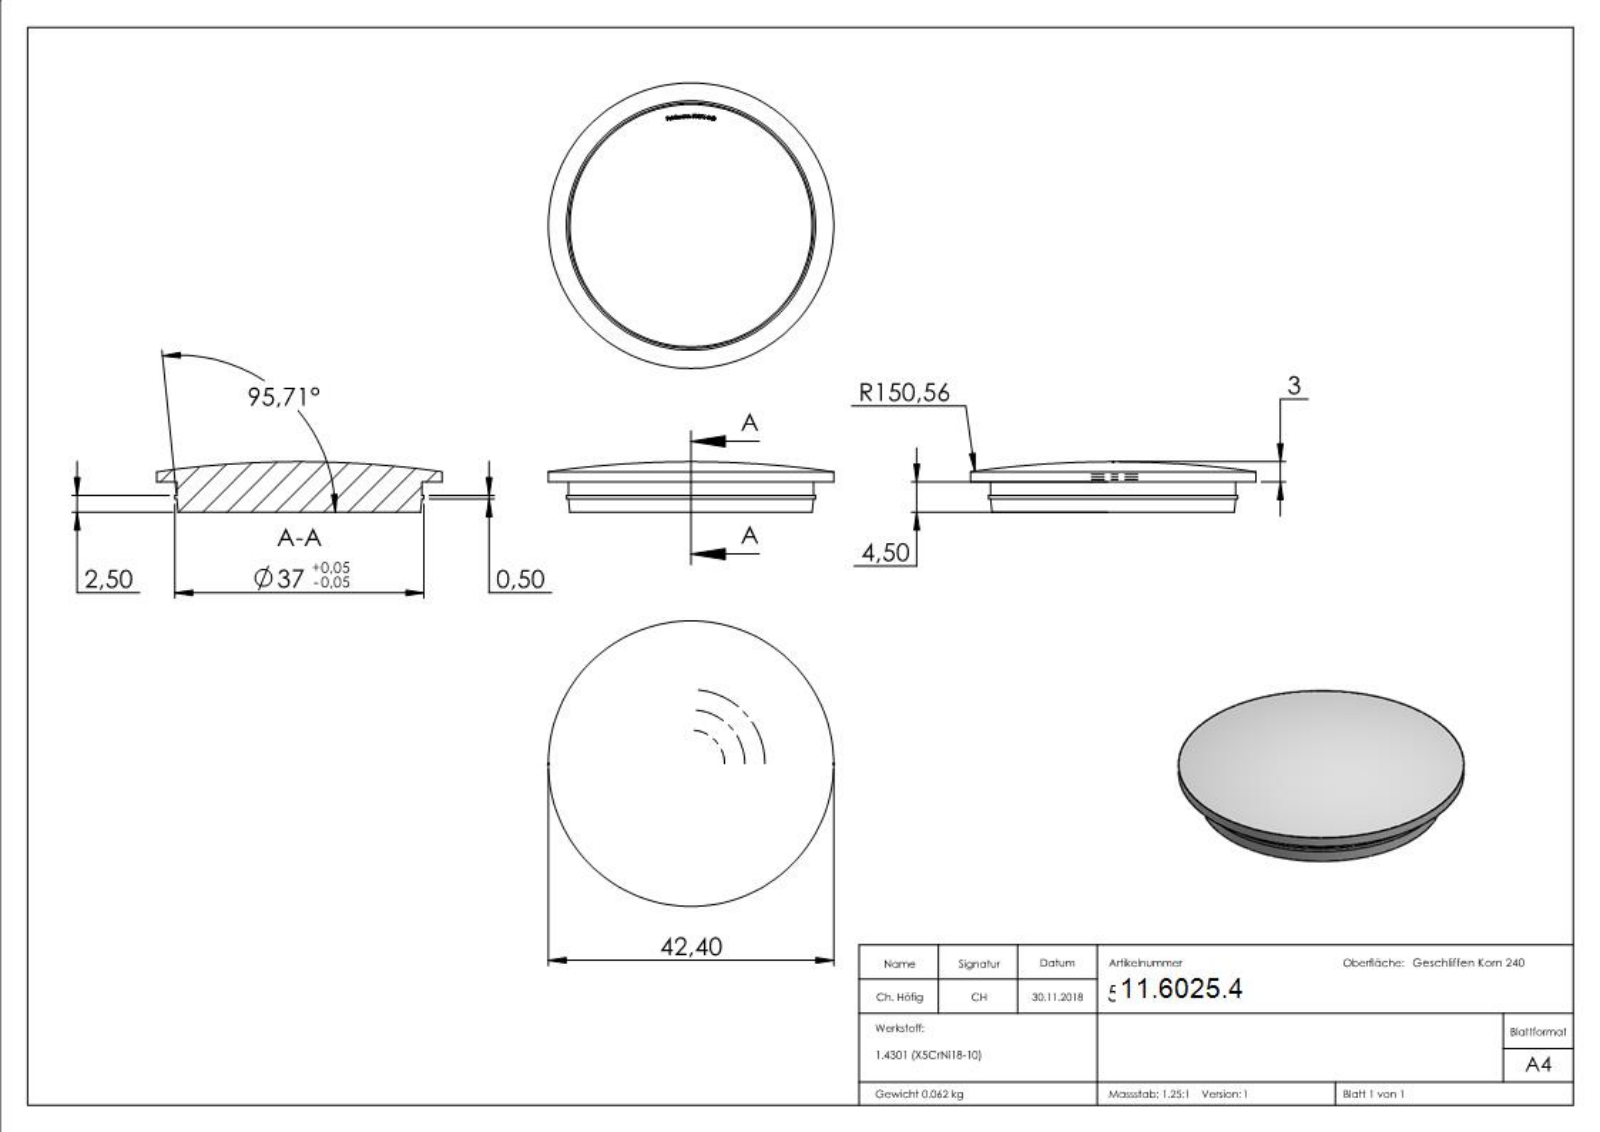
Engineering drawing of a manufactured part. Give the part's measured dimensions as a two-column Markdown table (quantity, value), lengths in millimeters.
| quantity | value |
| --- | --- |
| part name | 50876-240 |
| STEP written by | SolidWorks 2015 (CONFIG_CONTROL_DESIGN) |
| units | millimeters |
| bodies | 1 solid, 238 faces (122 planar, 6 cylindrical, 110 other) |
| overall size | 42.4 × 42.4 × 7.5 |
| volume | 7 855 mm³ |
| surface area | 3 612 mm² |
| round bosses / shafts (diameter × count) | 42.4 × 1, 37 × 1, 36.4 × 1 |
| main face-to-face distances | 4.5, 2, 2.5, 0.5, 1.5, 4, 0.53, 0.31, 0.58, 0.48 |
